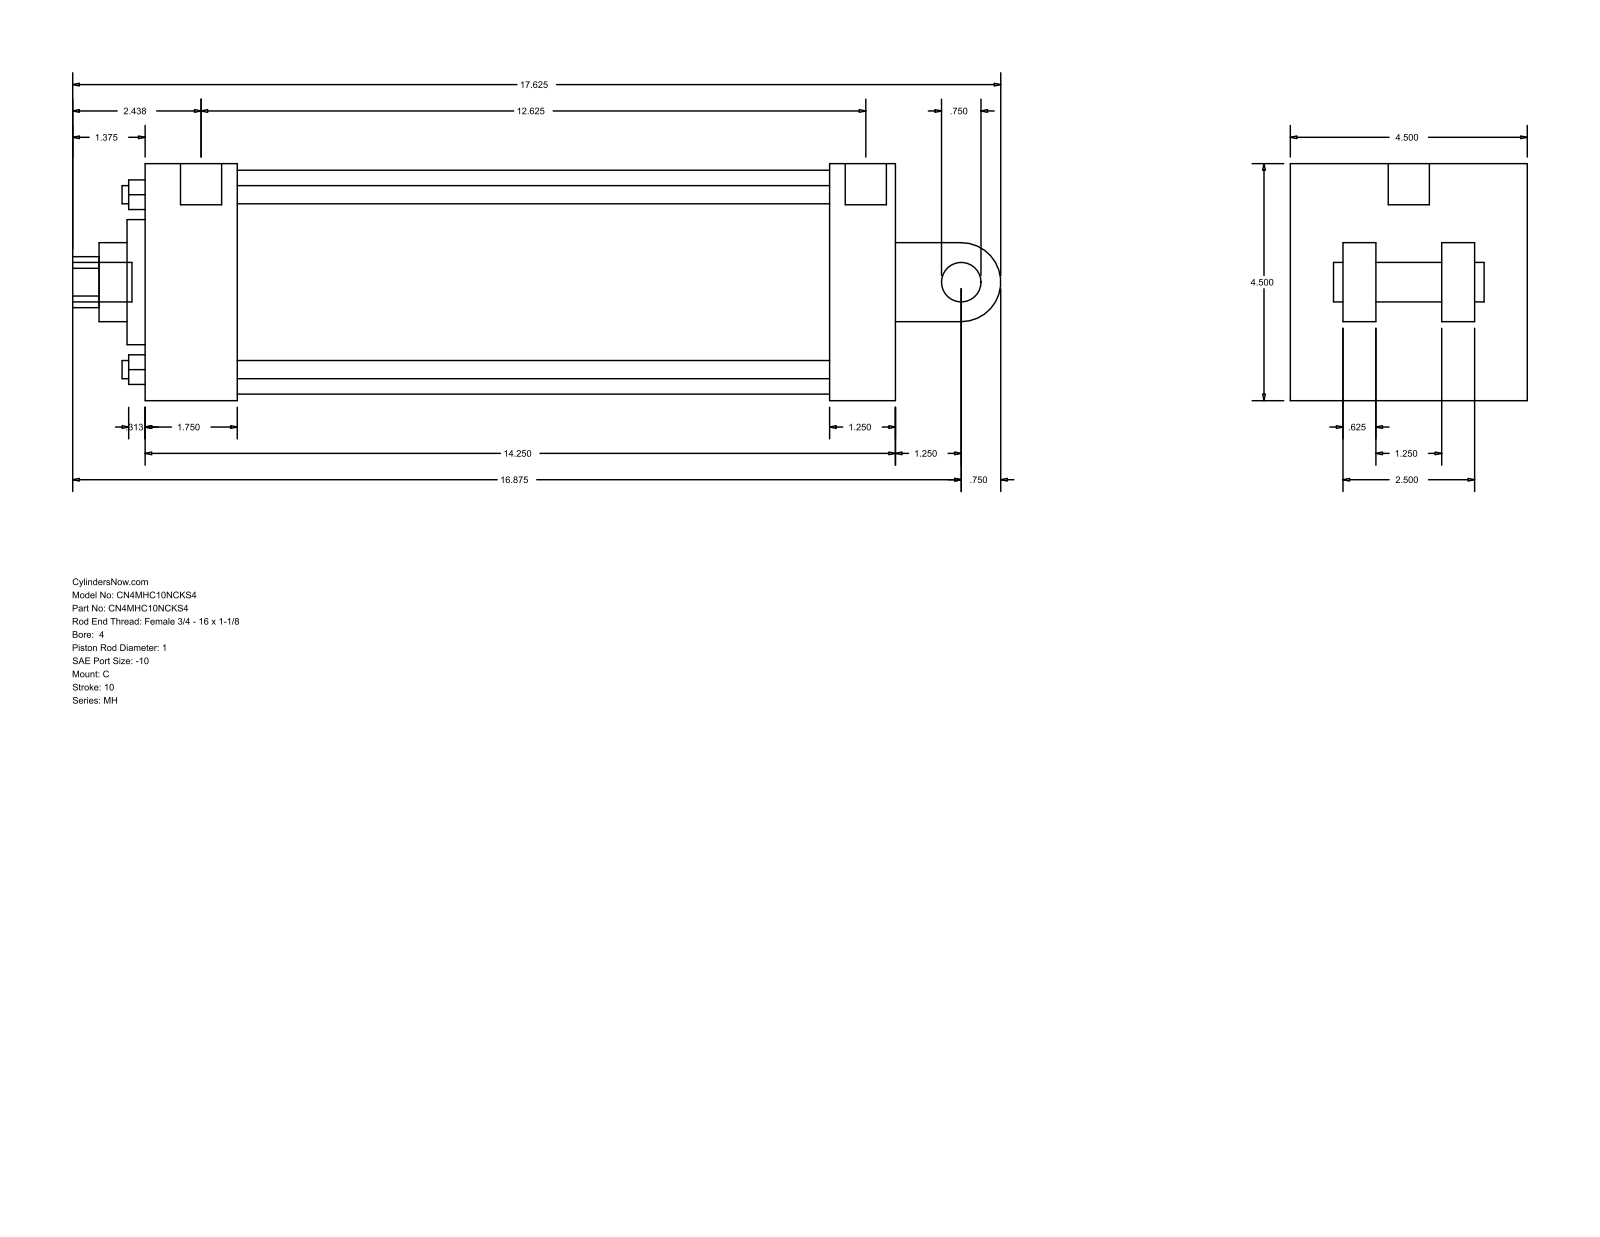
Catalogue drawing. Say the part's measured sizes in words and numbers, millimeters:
The part is named "MH_C__0400_1". Its 3-D file was written by "GSSL Pune (CONFIG_CONTROL_DESIGN)". It is 0 solids with 101 faces: 71 planar, 30 cylindrical and 0 other. Overall it measures 447.68 by 114.3 by 114.3 millimeters. Round holes: 4 of diameter 8.76, 2 of diameter 8.73, 1 of diameter 19.84, 1 of diameter 25.4, 1 of diameter 38.1, 1 of diameter 60.33, 1 of diameter 107.95. Round bosses or shafts: 2 of diameter 19.05, 2 of diameter 8.73, 1 of diameter 19.84. Partial cylindrical surfaces (rounded edges, fillets, slot ends): 1 of radius 12.29, 1 of radius 19.05. The main face-to-face distances are 114.3, 361.96, 31.76, 44.46, 330.2, 285.74, 317.5, 73.03, 15.87, 47.63. The hole center spacings are 59.62, 84.32, 119.25, 1.59.
